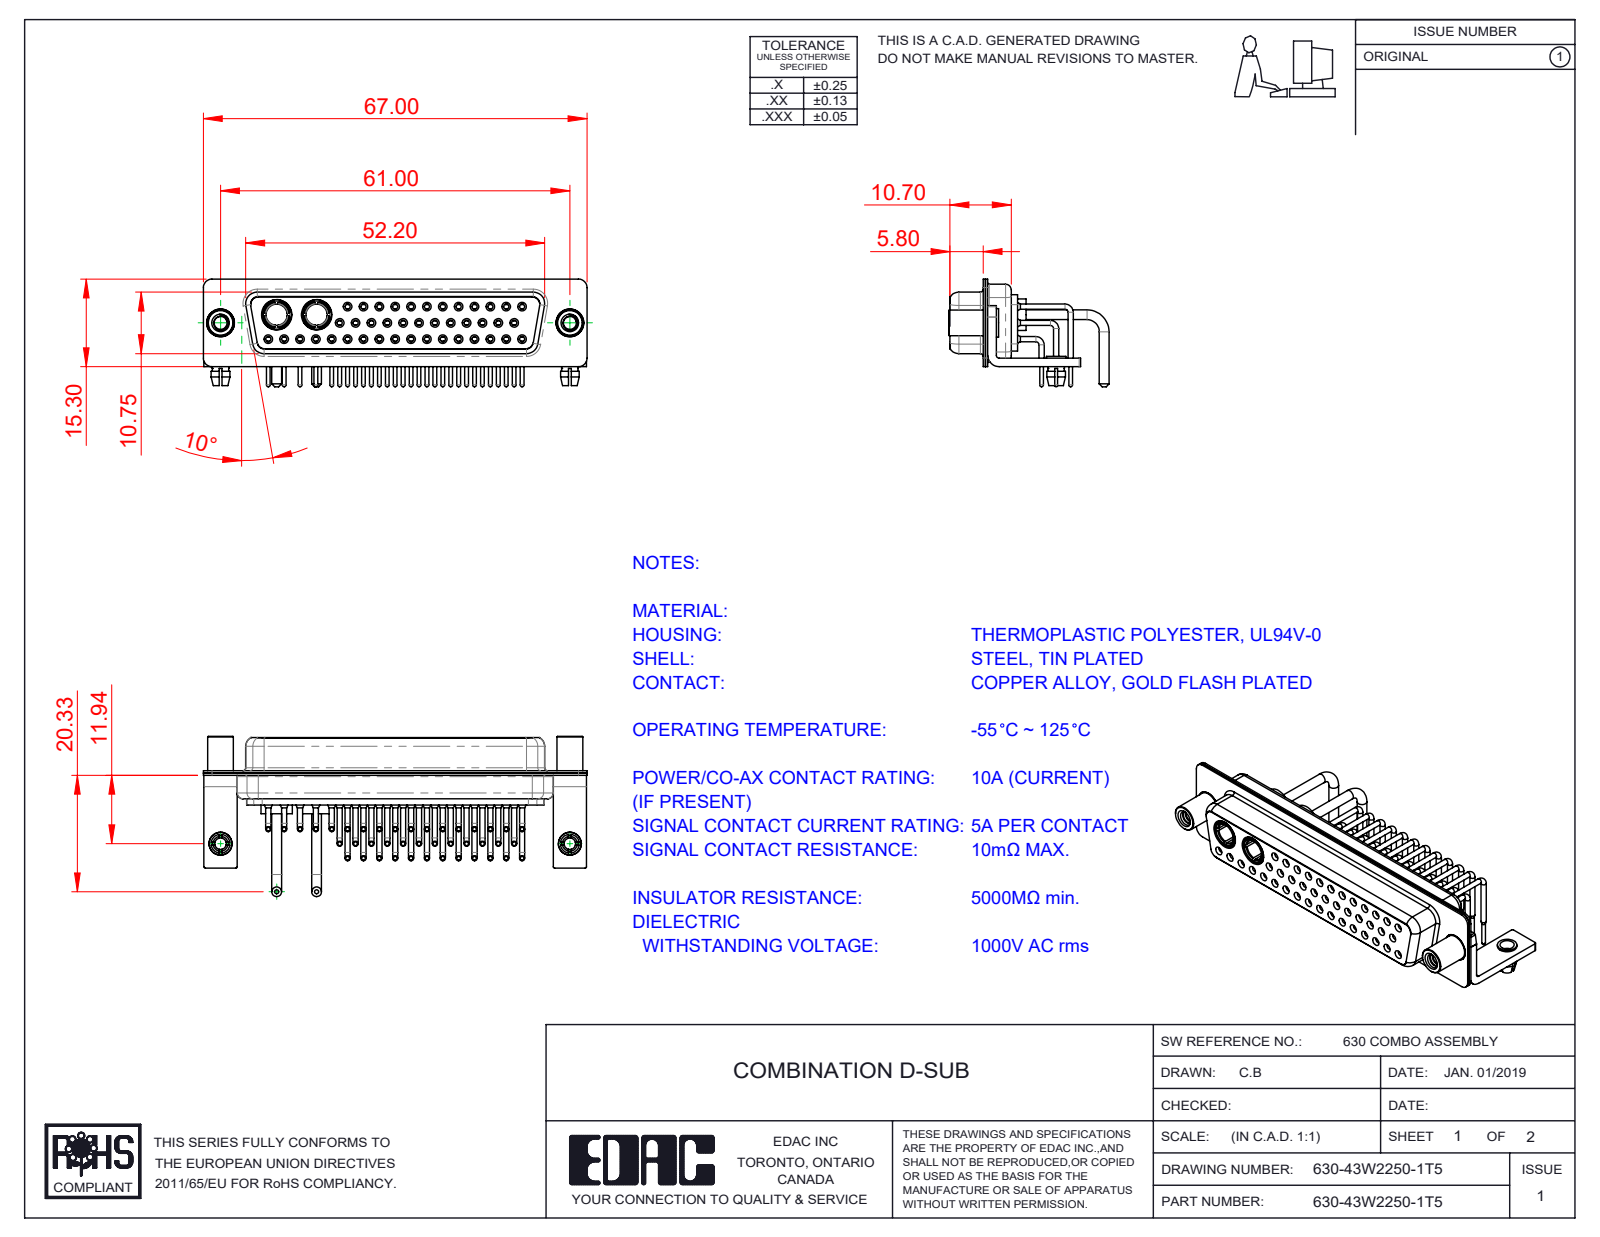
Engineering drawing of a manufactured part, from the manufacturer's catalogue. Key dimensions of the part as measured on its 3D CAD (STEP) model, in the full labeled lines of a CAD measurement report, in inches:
Part name (STEP PRODUCT): 630Combo Housing_43W2; 630Combo Contact Row 3; 630Combo Shell Rear_50 Contacts; 630Combo Contact Row 1_50 Contacts (+7 more)
STEP written by: SolidWorks 2020 (CONFIG_CONTROL_DESIGN)
Units: inches
Bodies: 54 solids, 2788 faces (810 planar, 1222 cylindrical, 756 other)
Overall size (bounding box): 2.638 × 1.102 × 0.74
Volume: 0.465 in³ · Surface area: 26.44 in²
Round holes (diameter × count): ⌀0.079 ×43, ⌀0.035 ×41, ⌀0.043 ×41, ⌀0.059 ×41, ⌀0.063 ×29, ⌀0.067 ×12, ⌀0.191 ×4, ⌀0.089 ×2, ⌀0.098 ×2, ⌀0.126 ×2, ⌀0.146 ×2, ⌀0.157 ×2
Round bosses / shafts (diameter × count): ⌀0.035 ×41, ⌀0.026 ×41, ⌀0.063 ×12, ⌀0.067 ×4, ⌀0.217 ×2, ⌀0.205 ×2, ⌀0.197 ×2, ⌀0.195 ×2
Partial cylindrical surfaces — rounded edges, fillets, slot ends (radius × count): R0.01 ×16, R0.059 ×16, R0.079 ×13, R0.053 ×12, R0.063 ×8, R0.02 ×5, R0.024 ×4, R0.026 ×4
Main face-to-face distances: 0.016, 0.059, 0.236, 0.22, 0.031, 0.205, 0.228, 0.444, 0.072, 0.244
Hole centre spacings: 0.109, 0.124, 0.218, 0.327, 0.436, 0.545, 0.654, 0.763
